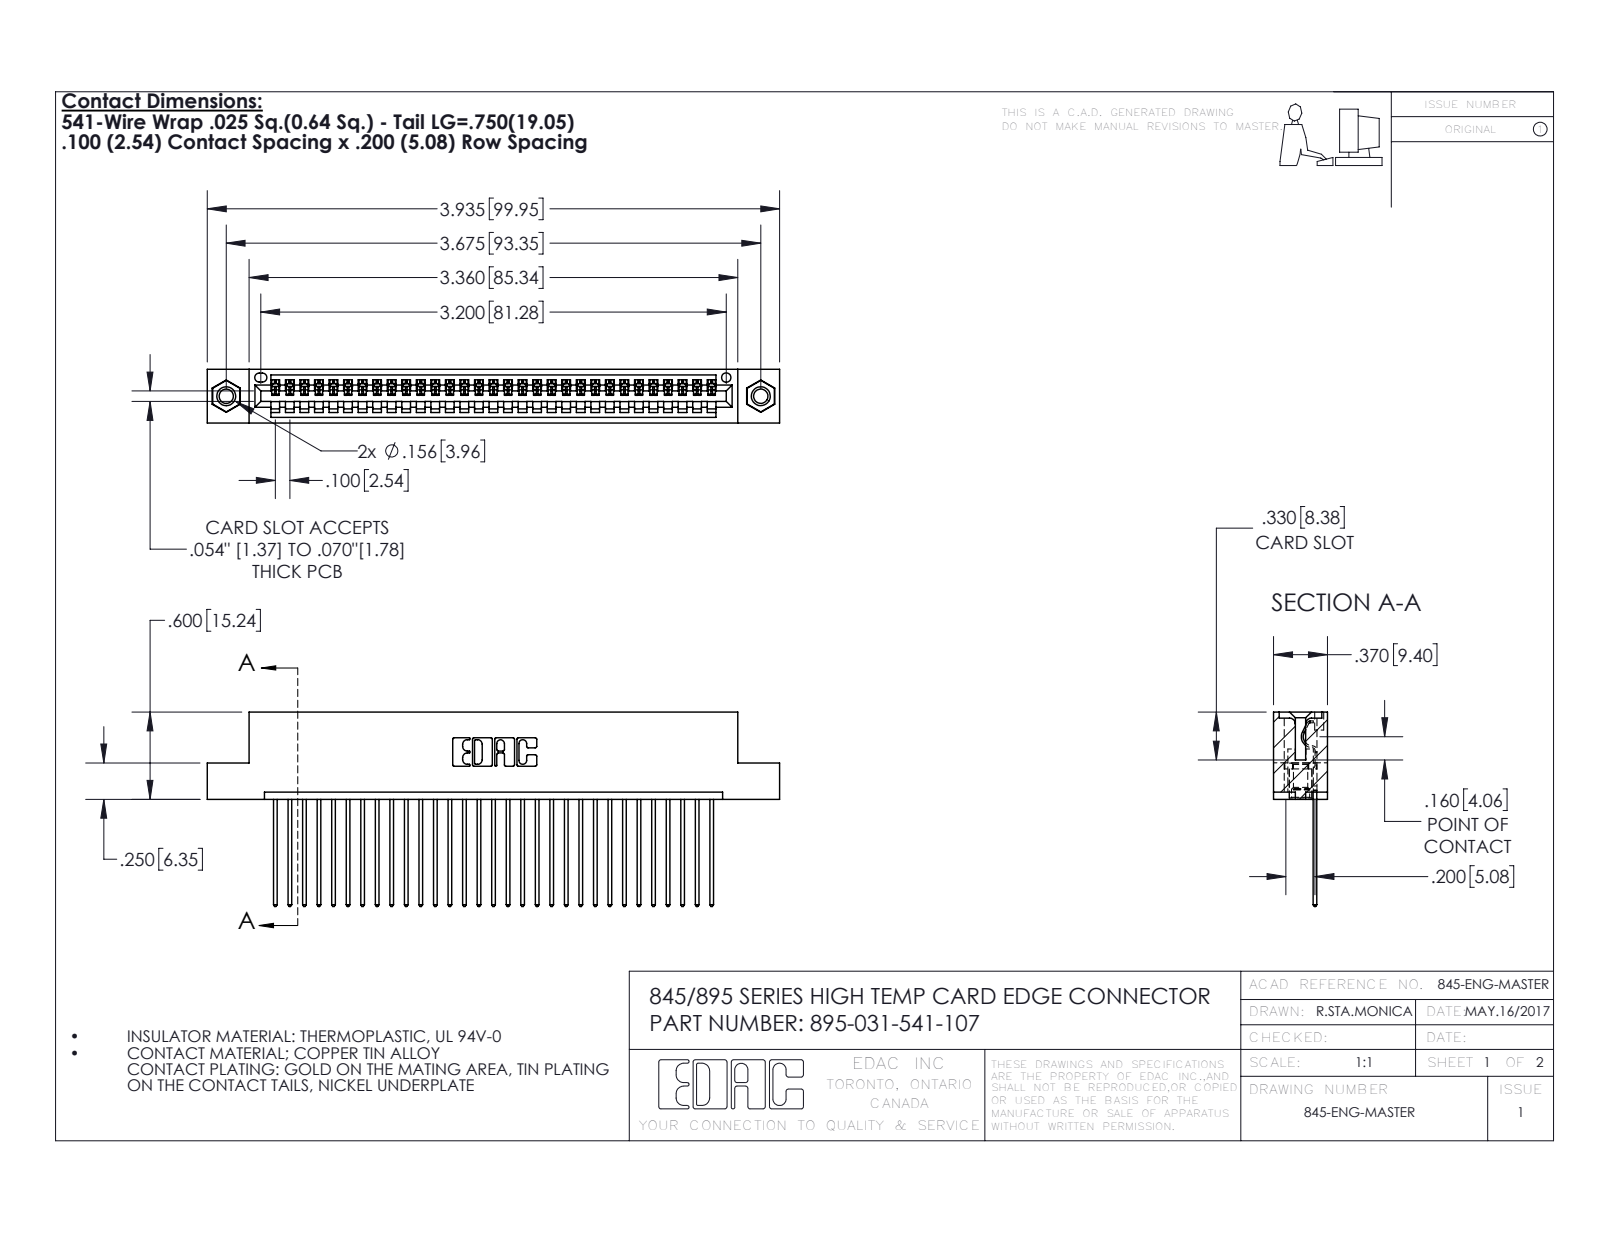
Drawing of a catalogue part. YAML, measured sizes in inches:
part_name: "345-292-001_345-293-141; 345 Part_Flush Mounting Lugs - 0.156 Dia-TI; 395-031-541-107; 345-250-001_345-250-005-103"
step_written_by: "SolidWorks 2016 (CONFIG_CONTROL_DESIGN)"
units: inches
bodies: {solids: 34, faces: 1984, planar: 1352, cylindrical: 616, other: 16}
overall_size: [3.935, 1.337, 0.37]
volume: 0.579
surface_area: 20.3
round_holes:
  - {diameter: 0.098, count: 2}
  - {diameter: 0.125, count: 2}
  - {diameter: 0.156, count: 2}
  - {diameter: 0.064, count: 1}
round_bosses_or_shafts:
  - {diameter: 0.155, count: 2}
partial_cylinders:
  - {radius: 0.006, count: 62}
  - {radius: 0.01, count: 62}
  - {radius: 0.01, count: 22}
  - {radius: 0.007, count: 6}
  - {radius: 0.031, count: 6}
  - {radius: 0.026, count: 3}
  - {radius: 0.031, count: 2}
  - {radius: 0.04, count: 2}
face_to_face_distances: [0.072, 0.298, 0.2, 0.37, 0.098, 0.272, 0.025, 0.225, 0.149, 0.072]
hole_center_spacings: [0.27, 3.44, 3.675]
